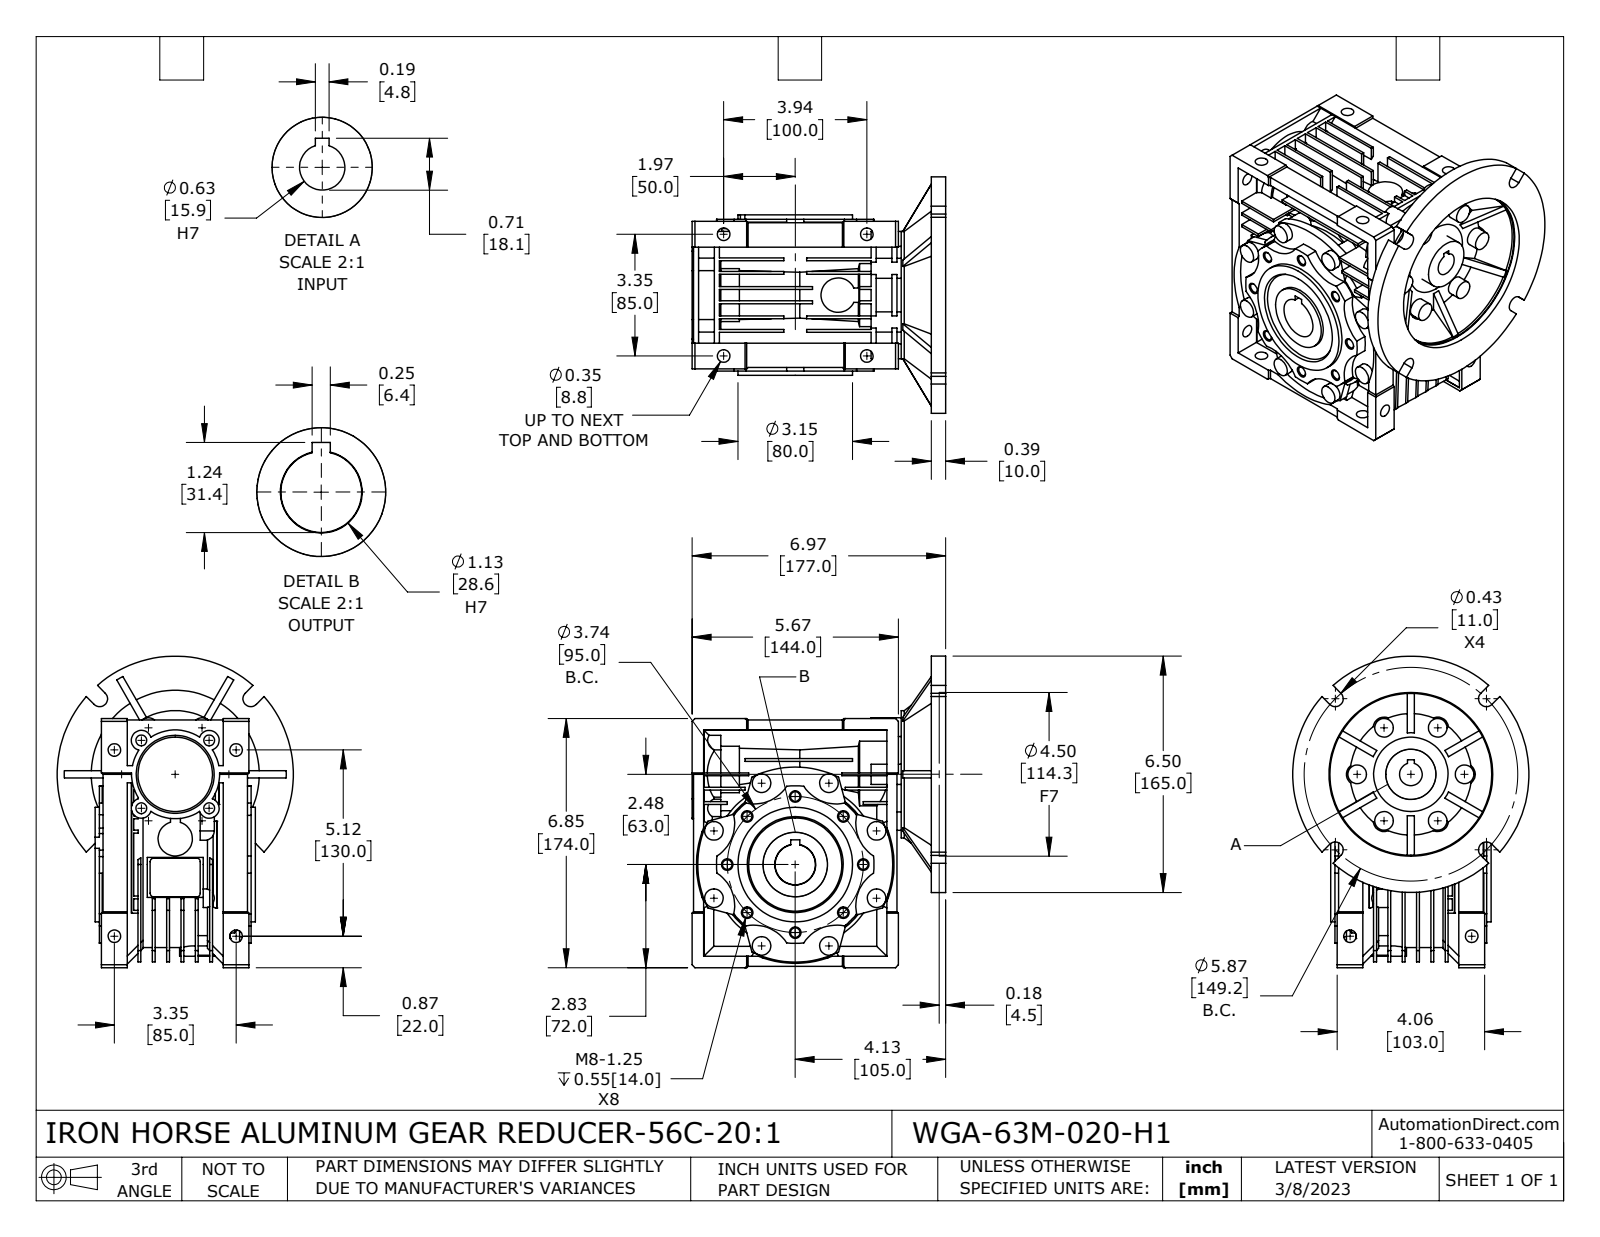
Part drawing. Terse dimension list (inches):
name: WGA-63M-020-H1
written by: SolidWorks 2021 (CONFIG_CONTROL_DESIGN)
unit: in
bodies: 4 solids, 1231 faces (759 planar, 331 cylindrical, 141 other)
size: 8.563 × 6.969 × 6.496
volume: 117 in³; area: 568 in²
holes: 8× ⌀0.262, 8× ⌀0.262, 8× ⌀0.346, 4× ⌀0.298, 1× ⌀0.625, 1× ⌀0.65, 1× ⌀1.125, 1× ⌀1.339, 1× ⌀1.457, 1× ⌀1.772, 1× ⌀2.047, 1× ⌀4.449
bosses: 14× ⌀0.512, 3× ⌀0.945, 1× ⌀6.496, 1× ⌀4.331, 1× ⌀3.504, 1× ⌀3.15, 1× ⌀2.717, 1× ⌀2.441
rounds: 10× R0.276, 8× R1.063, 6× R0.295, 4× R0.098, 4× R0.217, 1× R0.329, 1× R1.161, 1× R1.201
face distances: 0.394, 0.315, 0.787, 0.079, 1.181, 0.276, 0.472, 0.709, 1.575, 1.22
hole spacings: 1.431, 1.87, 2.645, 3.456, 1.319, 1.865, 3.346, 0.786
